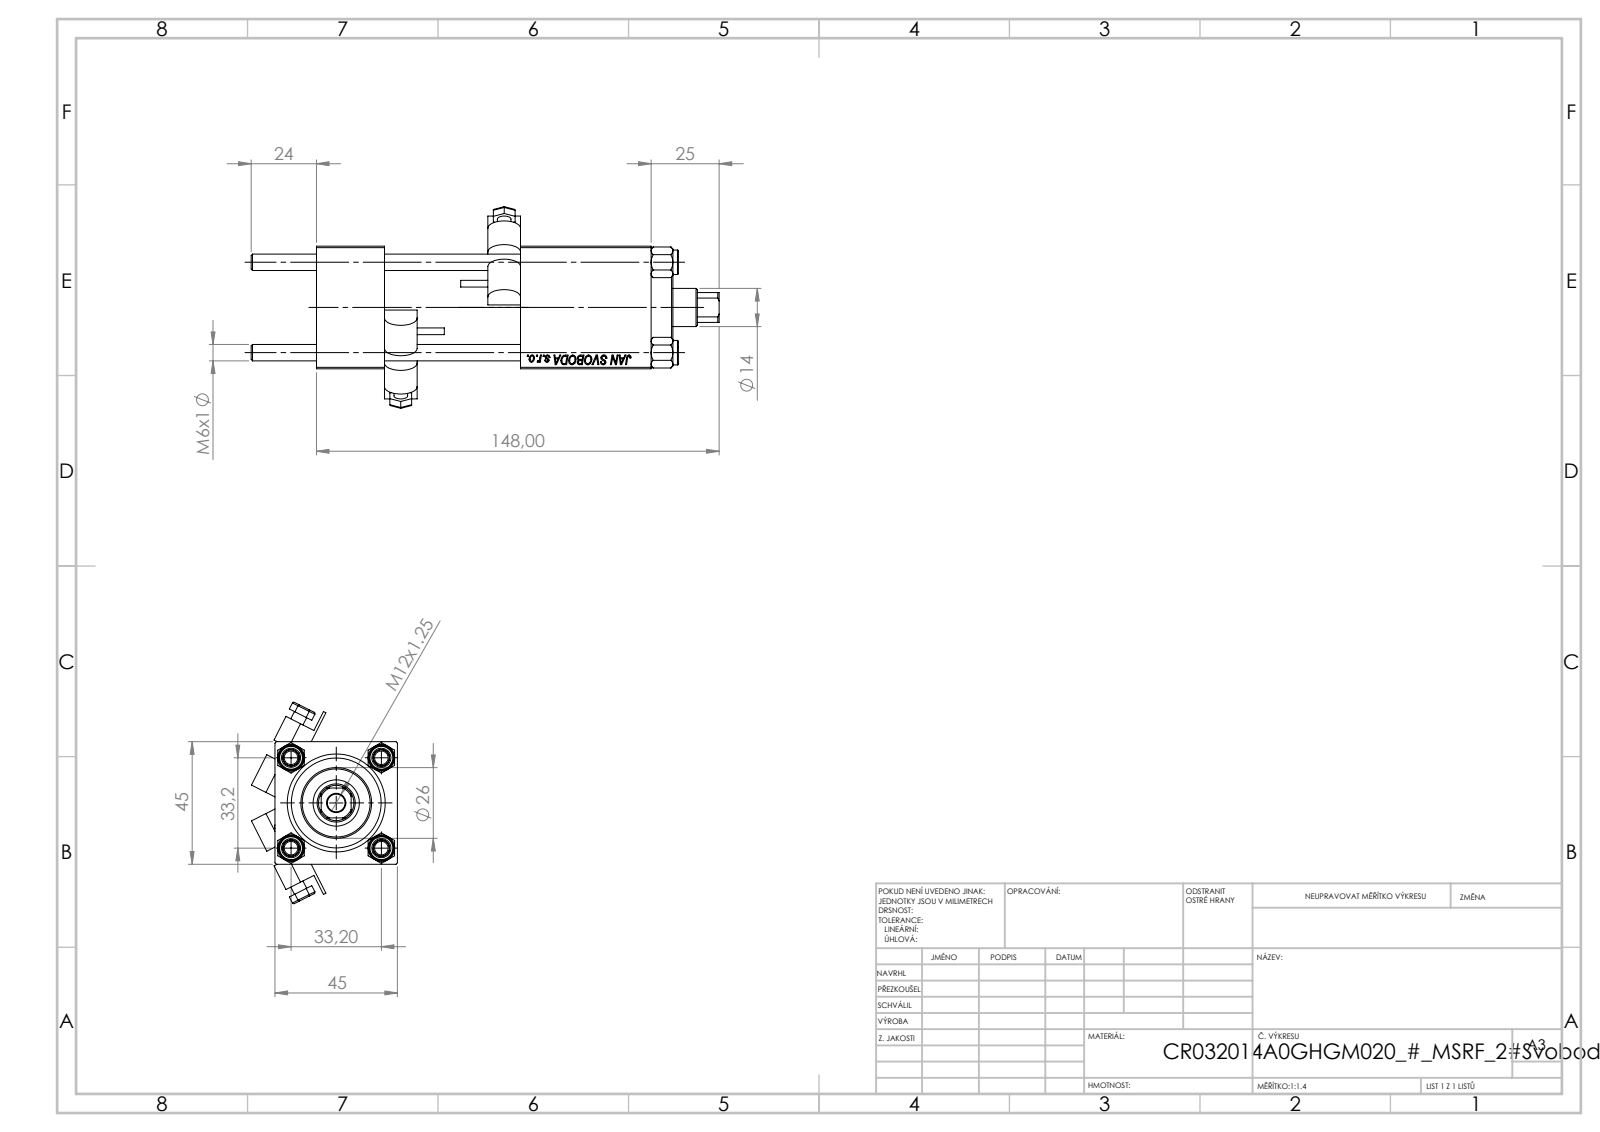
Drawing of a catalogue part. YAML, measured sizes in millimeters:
part_name: "V215_VC_A; V215CR_BODY_A; CR025_012_A_0_G_A_G_M_020_+#_##_TYCINKA; MSRF_MSRG1 (+2 more)"
step_written_by: "SolidWorks 2019 (CONFIG_CONTROL_DESIGN)"
units: millimeters
bodies: {solids: 13, faces: 1197, planar: 555, cylindrical: 106, other: 536}
overall_size: [172, 74.05, 53.66]
volume: 205265
surface_area: 77021
round_holes:
  - {diameter: 6, count: 4}
  - {diameter: 7, count: 2}
  - {diameter: 13.16, count: 2}
  - {diameter: 20, count: 2}
  - {diameter: 6.5, count: 1}
  - {diameter: 14, count: 1}
  - {diameter: 17, count: 1}
  - {diameter: 24, count: 1}
  - {diameter: 32, count: 1}
  - {diameter: 33, count: 1}
round_bosses_or_shafts:
  - {diameter: 9, count: 4}
  - {diameter: 5, count: 2}
  - {diameter: 2.5, count: 2}
  - {diameter: 38, count: 1}
  - {diameter: 26, count: 1}
partial_cylinders:
  - {radius: 0.5, count: 12}
  - {radius: 6, count: 4}
  - {radius: 6.5, count: 1}
face_to_face_distances: [45, 25, 123, 98, 50, 48, 75, 94.3, 69.3, 19.3]
hole_center_spacings: [23.48, 33.2, 46.95, 75.5]
